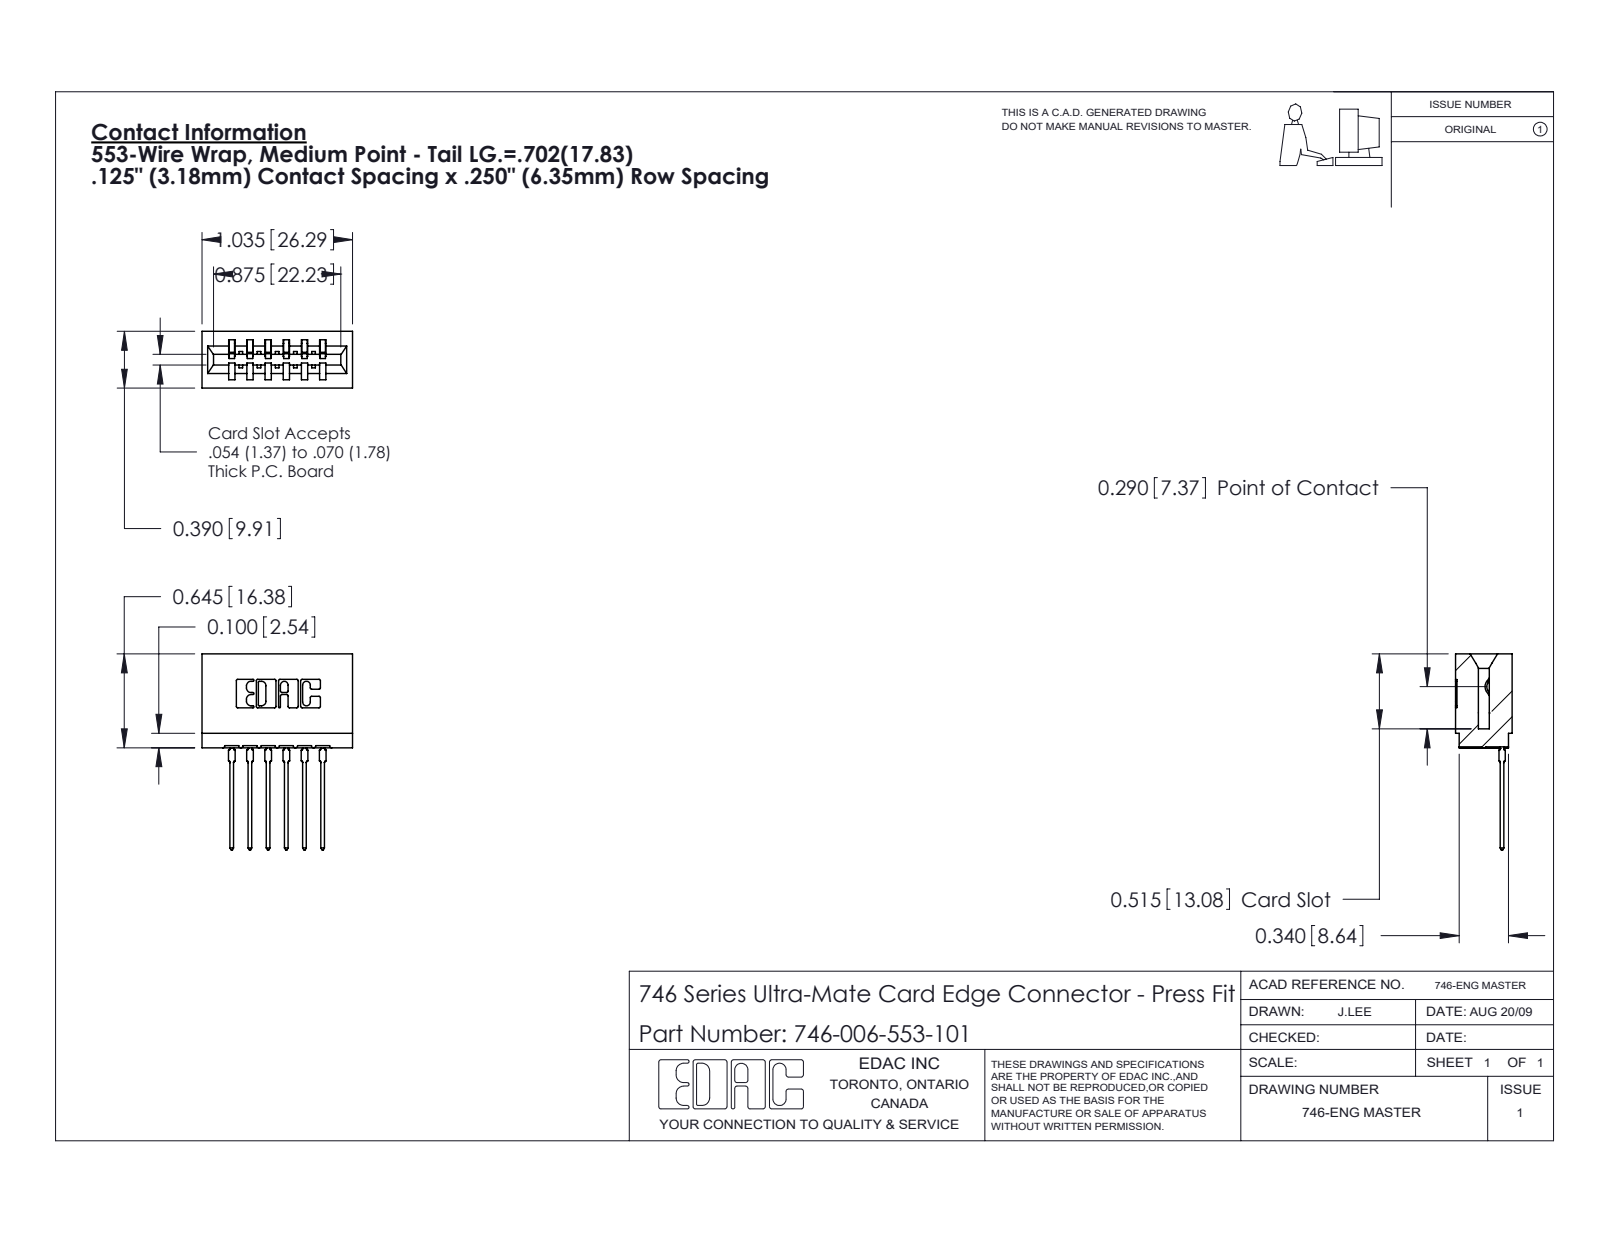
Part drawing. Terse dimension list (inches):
name: 746-292-001_553; 746 Part_.515 Slot Depth - 01; 746-006-553-101
written by: SolidWorks 2020 (CONFIG_CONTROL_DESIGN)
unit: in
bodies: 7 solids, 745 faces (433 planar, 156 cylindrical, 156 other)
size: 1.346 × 1.035 × 0.39
volume: 0.184 in³; area: 6.16 in²
rounds: 22× R0.01, 12× R0.021, 7× R0.015, 6× R0.007, 6× R0.031, 4× R0.005, 4× R0.011, 3× R0.026
face distances: 0.25, 0.125, 0.042, 0.333, 0.057, 0.39, 0.375, 0.292, 0.208, 0.125
